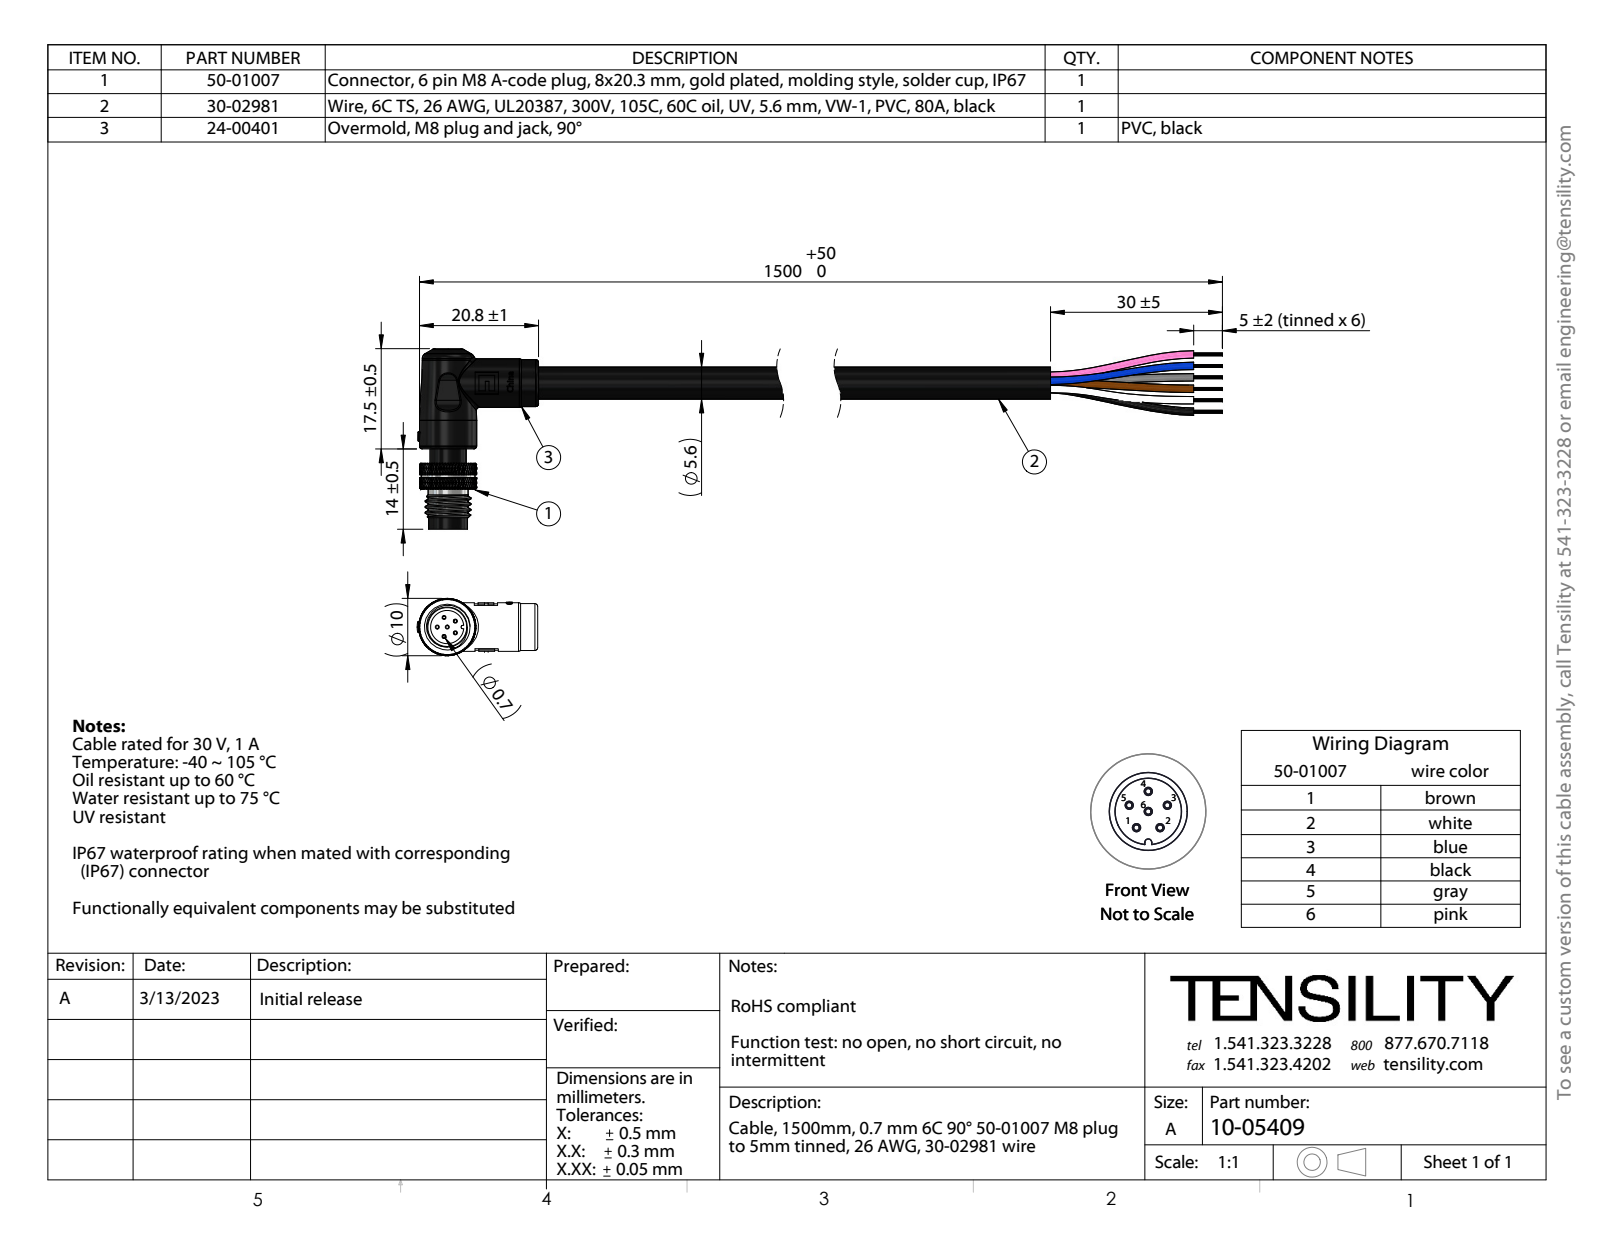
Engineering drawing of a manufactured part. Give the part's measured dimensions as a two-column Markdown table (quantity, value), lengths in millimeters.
| quantity | value |
| --- | --- |
| part name | 50-01007-02_STEP; 50-01007-01; 10-05408revA; 50-01007-03 (+4 more) |
| STEP written by | SolidWorks 2021 (CONFIG_CONTROL_DESIGN) |
| units | millimeters |
| bodies | 324 solids, 1987 faces (744 planar, 1074 cylindrical, 169 other) |
| overall size | 201.05 × 31.5 × 10 |
| volume | 6 405 mm³ |
| surface area | 32 370 mm² |
| round holes (diameter × count) | 0.6 × 6, 0.7 × 6, 1.3 × 6, 3.92 × 1, 4.12 × 1, 5.8 × 1, 6.4 × 1 |
| round bosses / shafts (diameter × count) | 1.1 × 6, 10 × 1, 9.4 × 1, 9 × 1, 8.5 × 1, 8.2 × 1, 8 × 1, 7 × 1 |
| partial cylindrical surfaces (radius × count) | 2.32 × 6, 0.3 × 1, 4.05 × 1, 4.25 × 1, 5 × 1 |
| main face-to-face distances | 4.5, 7, 2.5, 2, 9, 150, 5, 9.5, 6.3, 8.8 |
| hole center spacings | 0.38, 0.36, 2.55, 0.32, 0.35, 1.3, 1.53, 1.75 |
